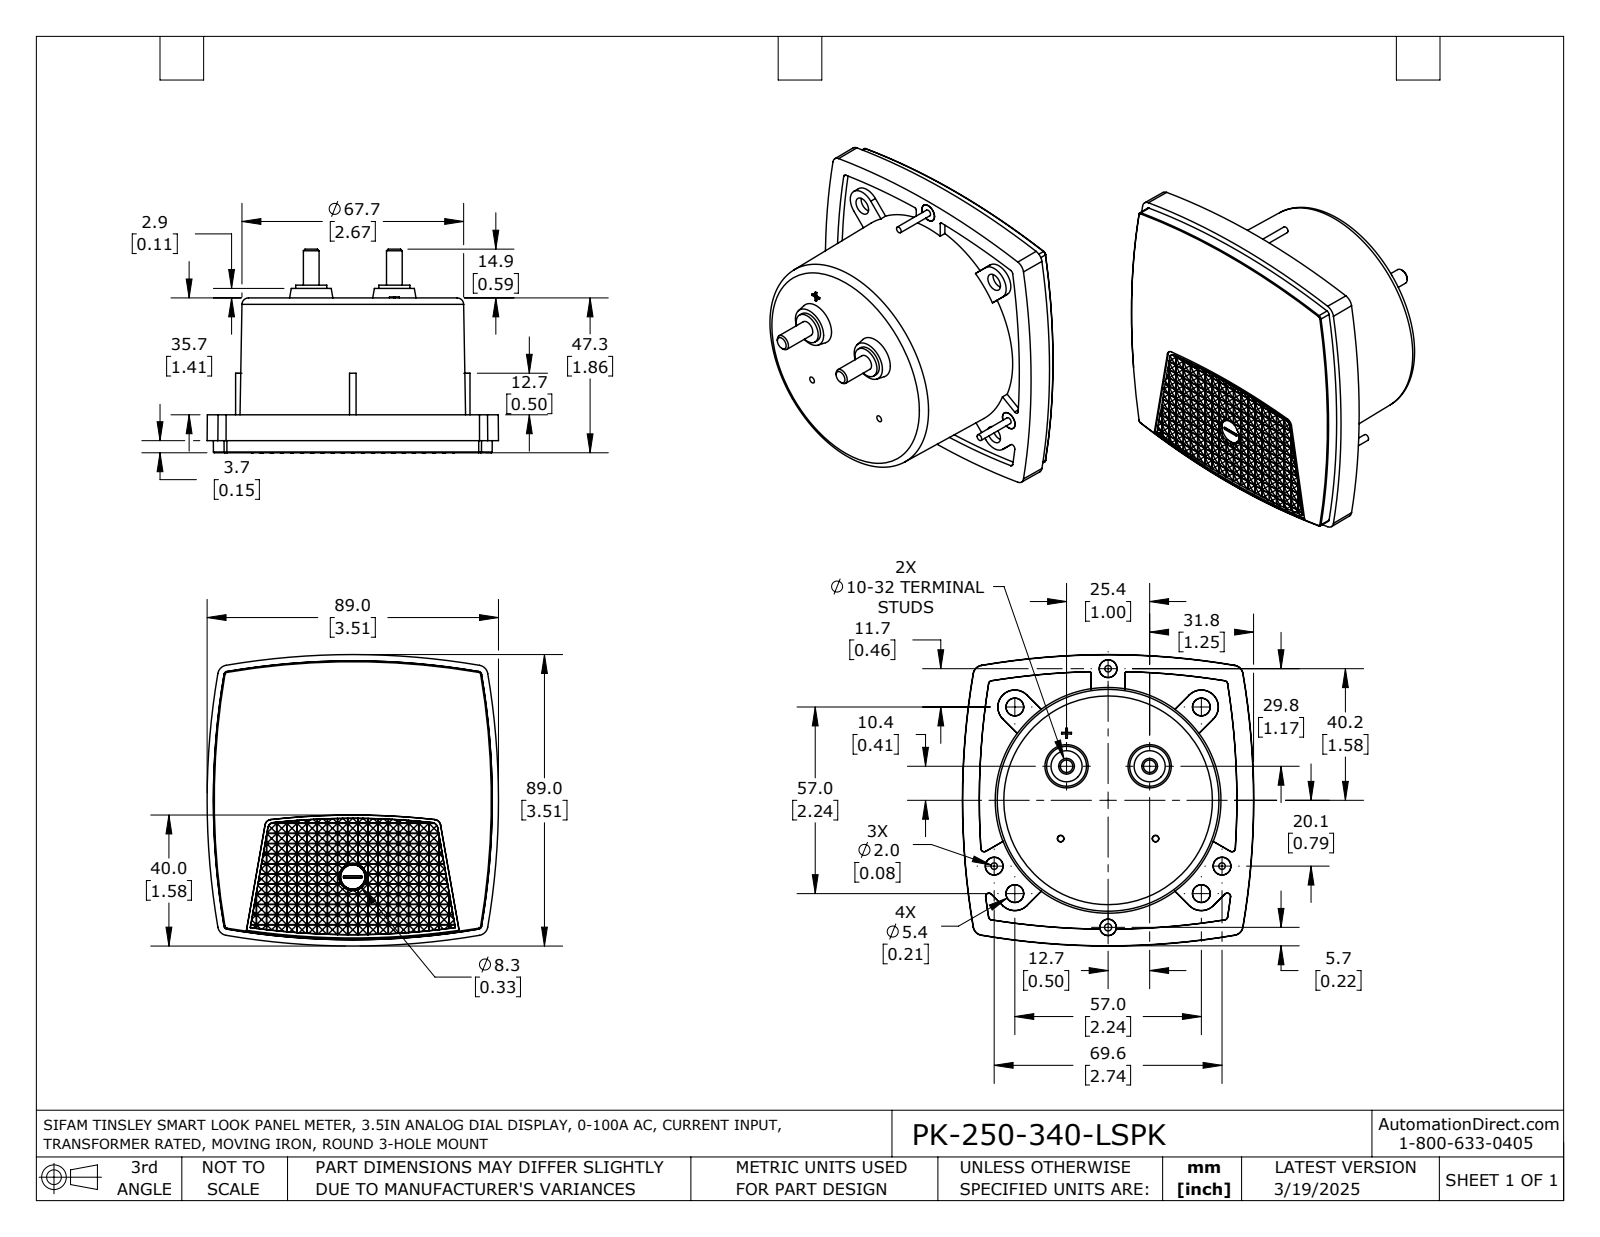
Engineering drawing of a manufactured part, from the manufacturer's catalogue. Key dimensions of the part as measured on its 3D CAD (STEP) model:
Part name (STEP PRODUCT): PK-250-340-LSPK
STEP written by: SolidWorks 2021 (AUTOMOTIVE_DESIGN)
Units: inches
Bodies: 1 solid, 1078 faces (950 planar, 23 cylindrical, 105 other)
Overall size (bounding box): 3.505 × 3.505 × 2.453
Volume: 12.99 in³ · Surface area: 44.29 in²
Round holes (diameter × count): ⌀0.087 ×1
Round bosses / shafts (diameter × count): ⌀0.213 ×3, ⌀0.079 ×3, ⌀0.374 ×2, ⌀0.189 ×2
Partial cylindrical surfaces — rounded edges, fillets, slot ends (radius × count): R8.961 ×1
Main face-to-face distances: 1.862, 1.406, 0.457, 0.079, 1.484, 0.378, 0.024, 0.096, 0.072, 0.12
